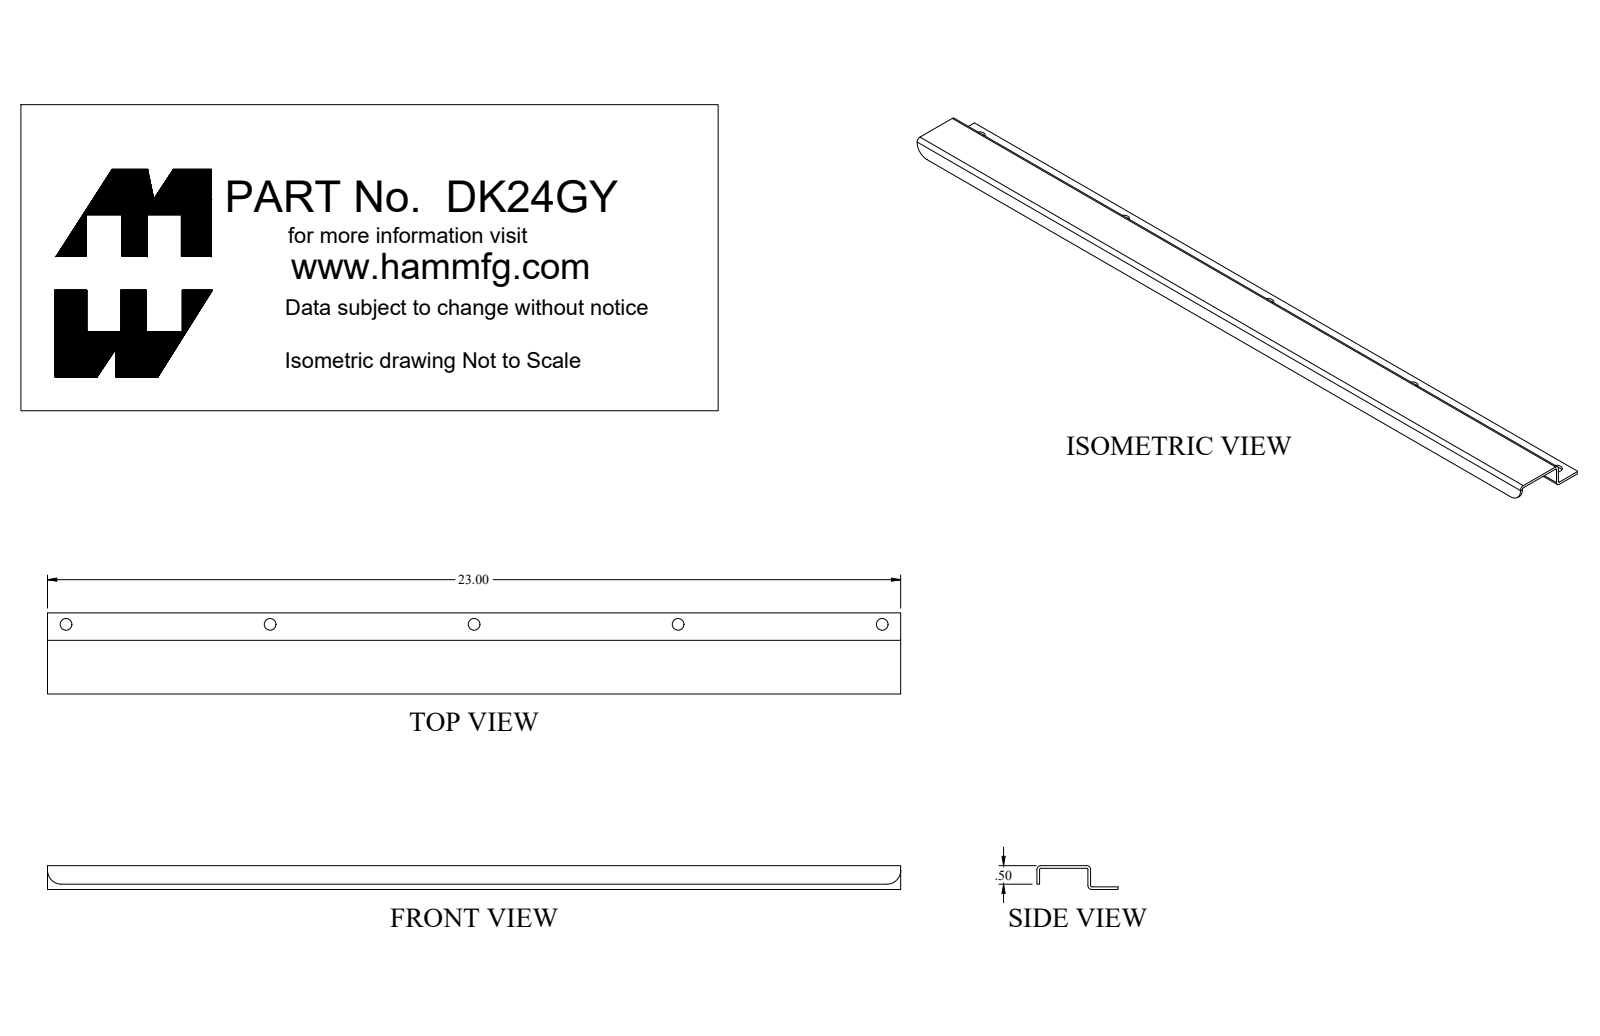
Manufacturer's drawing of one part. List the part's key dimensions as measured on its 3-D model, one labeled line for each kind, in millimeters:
Part name (STEP PRODUCT): DK24GY_Default
STEP written by: SolidWorks 2018 (CONFIG_CONTROL_DESIGN)
Units: millimetres
Bodies: 5 solids, 69 faces (35 planar, 28 cylindrical, 6 other)
Overall size (bounding box): 584.2 × 55.6 × 33.6
Volume: 103 100 mm³ · Surface area: 119 800 mm²
Round holes (diameter × count): ⌀8 ×5, ⌀5.1 ×1, ⌀7 ×1
Round bosses / shafts (diameter × count): ⌀15.9 ×1, ⌀12.3 ×1, ⌀6.4 ×1
Partial cylindrical surfaces — rounded edges, fillets, slot ends (radius × count): R0.9 ×3, R2.7 ×3, R9.5 ×2
Main face-to-face distances: 1.8, 14.5, 16.4, 35, 12.7, 1.6, 16.1, 18, 3.4, 36.8
Hole centre spacings: 139.7, 279.4, 419.1, 558.8
